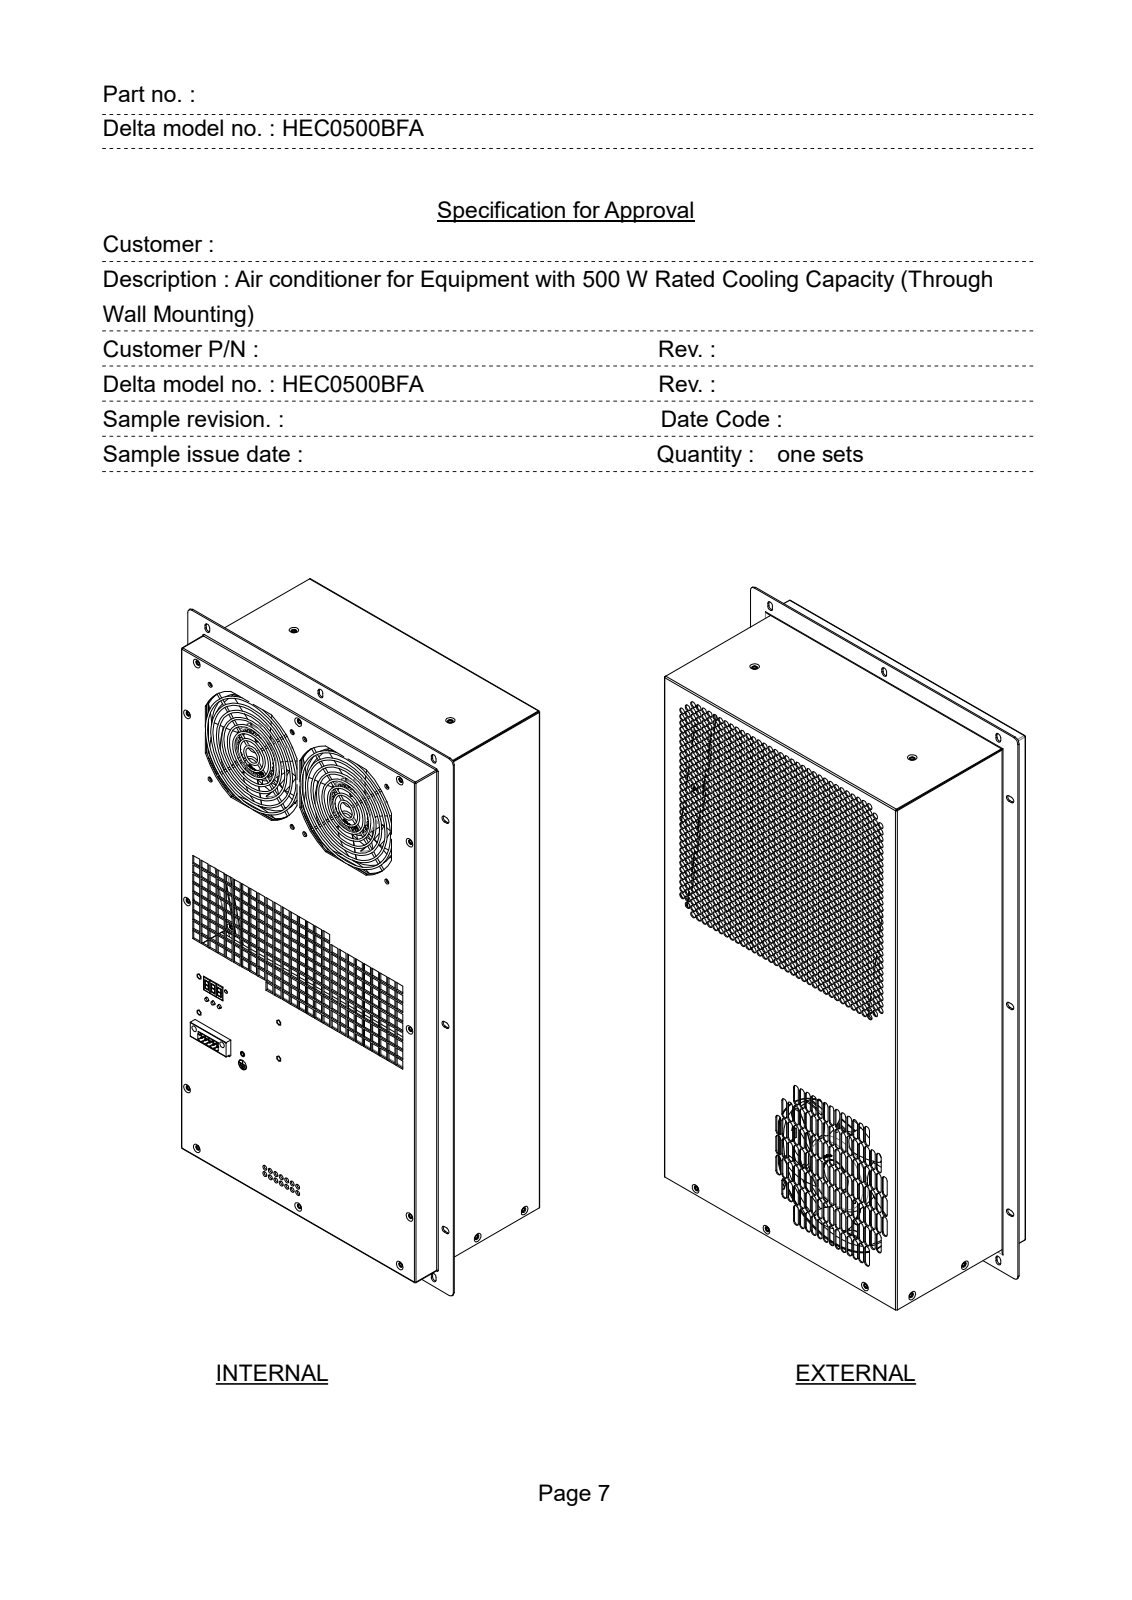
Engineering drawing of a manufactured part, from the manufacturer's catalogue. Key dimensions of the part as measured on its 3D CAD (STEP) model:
Part name (STEP PRODUCT): Drain pipe; 2EHDP-05P; CASE COVER 500W V1.0; HEC0500BFA (+5 more)
STEP written by: SolidWorks 2016 (CONFIG_CONTROL_DESIGN)
Units: millimetres
Bodies: 8 solids, 5009 faces (1664 planar, 3061 cylindrical, 284 other)
Overall size (bounding box): 594.5 × 339.5 × 168.2
Volume: 727 691 mm³ · Surface area: 1 301 000 mm²
Round holes (diameter × count): ⌀6 ×1247, ⌀5 ×22, ⌀4.5 ×21, ⌀3.4 ×15, ⌀4.2 ×7, ⌀4 ×3, ⌀3.2 ×2, ⌀5.7 ×2, ⌀10 ×2, ⌀3.5 ×1, ⌀8 ×1, ⌀12.1 ×1
Round bosses / shafts (diameter × count): ⌀2 ×8, ⌀12 ×1, ⌀9.6 ×1
Partial cylindrical surfaces — rounded edges, fillets, slot ends (radius × count): R3 ×263, R0.2 ×18, R1.2 ×18, R1 ×17, R2.5 ×6, R5 ×4, R0.1 ×2, R0.3 ×2
Main face-to-face distances: 1, 1.5, 294, 159.5, 160.5, 161, 162, 293, 549, 295
Hole centre spacings: 7, 14, 21, 28, 35, 42, 49, 56
